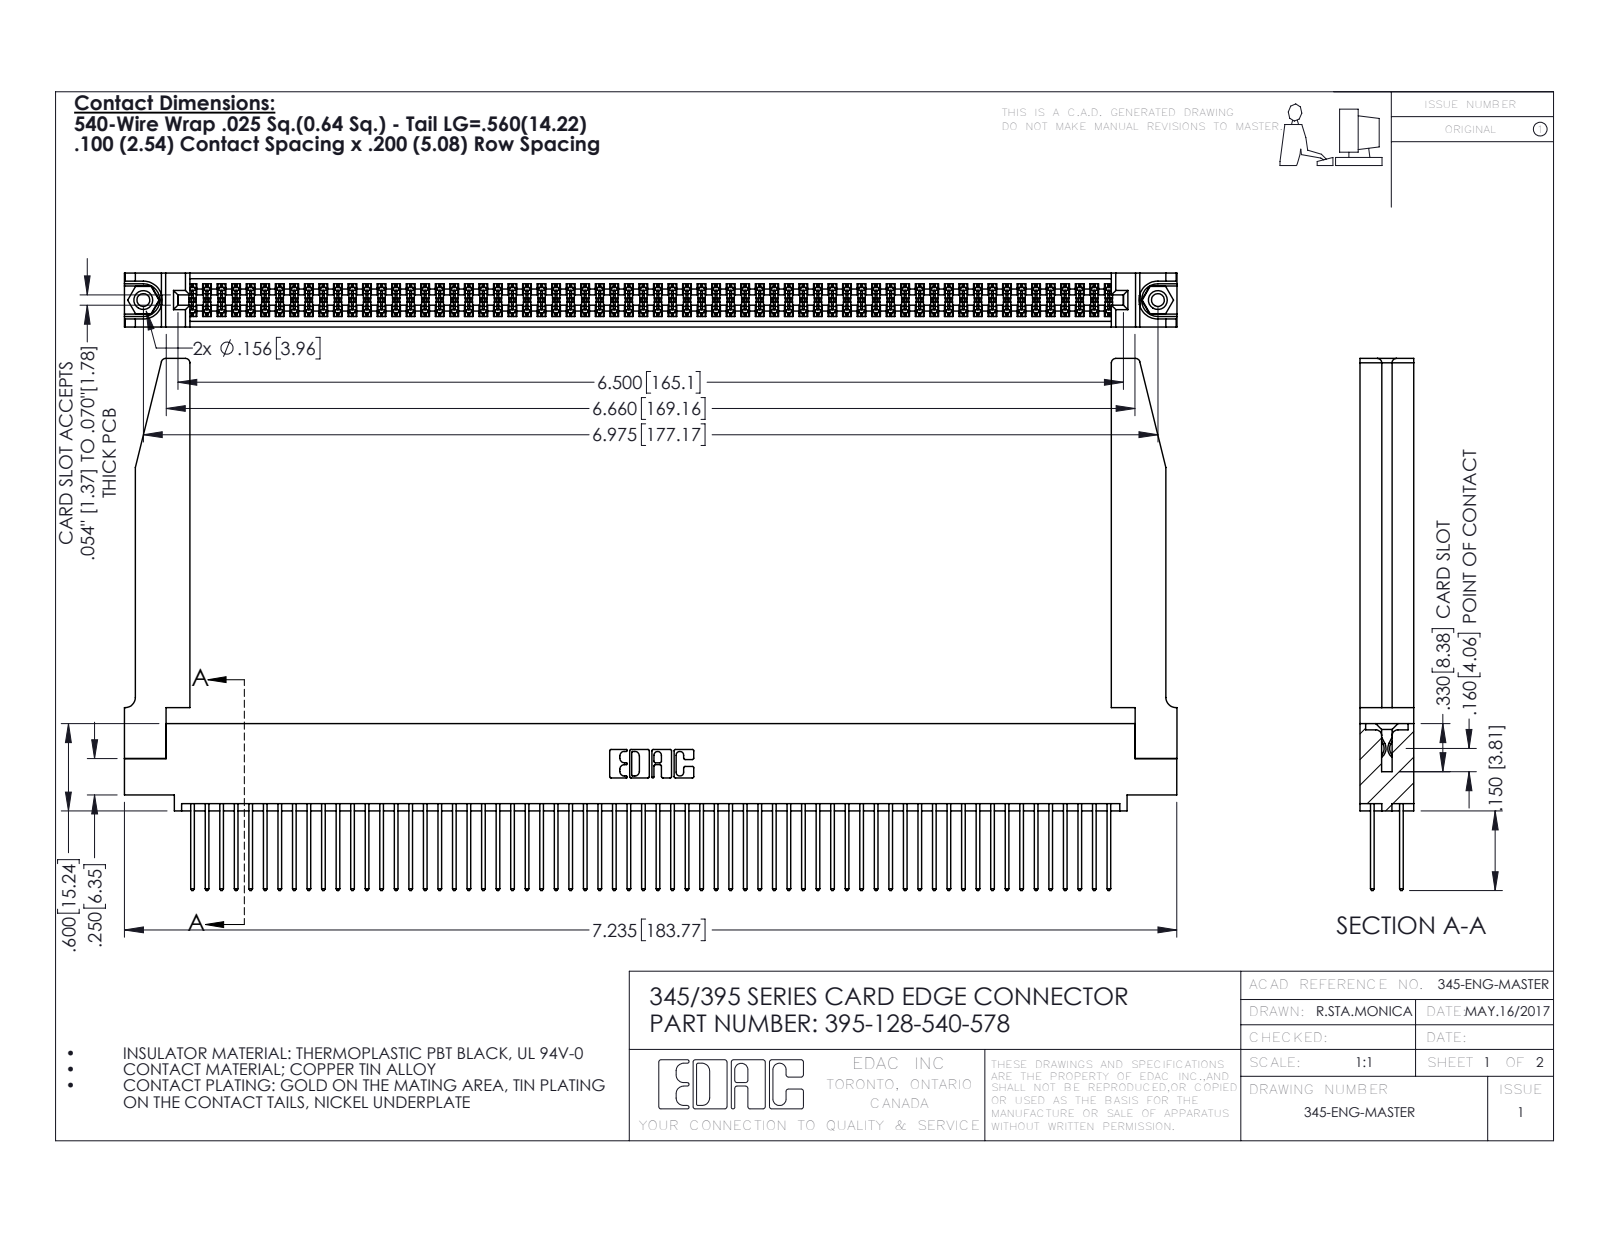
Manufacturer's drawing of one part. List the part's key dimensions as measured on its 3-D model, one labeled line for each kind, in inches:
Part name (STEP PRODUCT): 345-220-078_345-220-078; 395-128-540-578; 345 Part_0.110 Offset - 0.156 Dia-TH; 345-292-001_345-293-140 (+1 more)
STEP written by: SolidWorks 2016 (CONFIG_CONTROL_DESIGN)
Units: inches
Bodies: 133 solids, 6764 faces (4450 planar, 2262 cylindrical, 52 other)
Overall size (bounding box): 7.236 × 3.657 × 0.37
Volume: 1.601 in³ · Surface area: 57.21 in²
Round holes (diameter × count): ⌀0.089 ×2, ⌀0.125 ×2, ⌀0.156 ×2, ⌀0.064 ×1
Round bosses / shafts (diameter × count): ⌀0.155 ×2
Partial cylindrical surfaces — rounded edges, fillets, slot ends (radius × count): R0.006 ×192, R0.01 ×128, R0.01 ×22, R0.03 ×8, R0.007 ×6, R0.031 ×6, R0.026 ×3, R0.014 ×2
Main face-to-face distances: 0.072, 0.298, 0.37, 0.098, 0.272, 0.025, 0.2, 0.225, 0.175, 0.148
Hole centre spacings: 0.27, 6.739, 6.975
